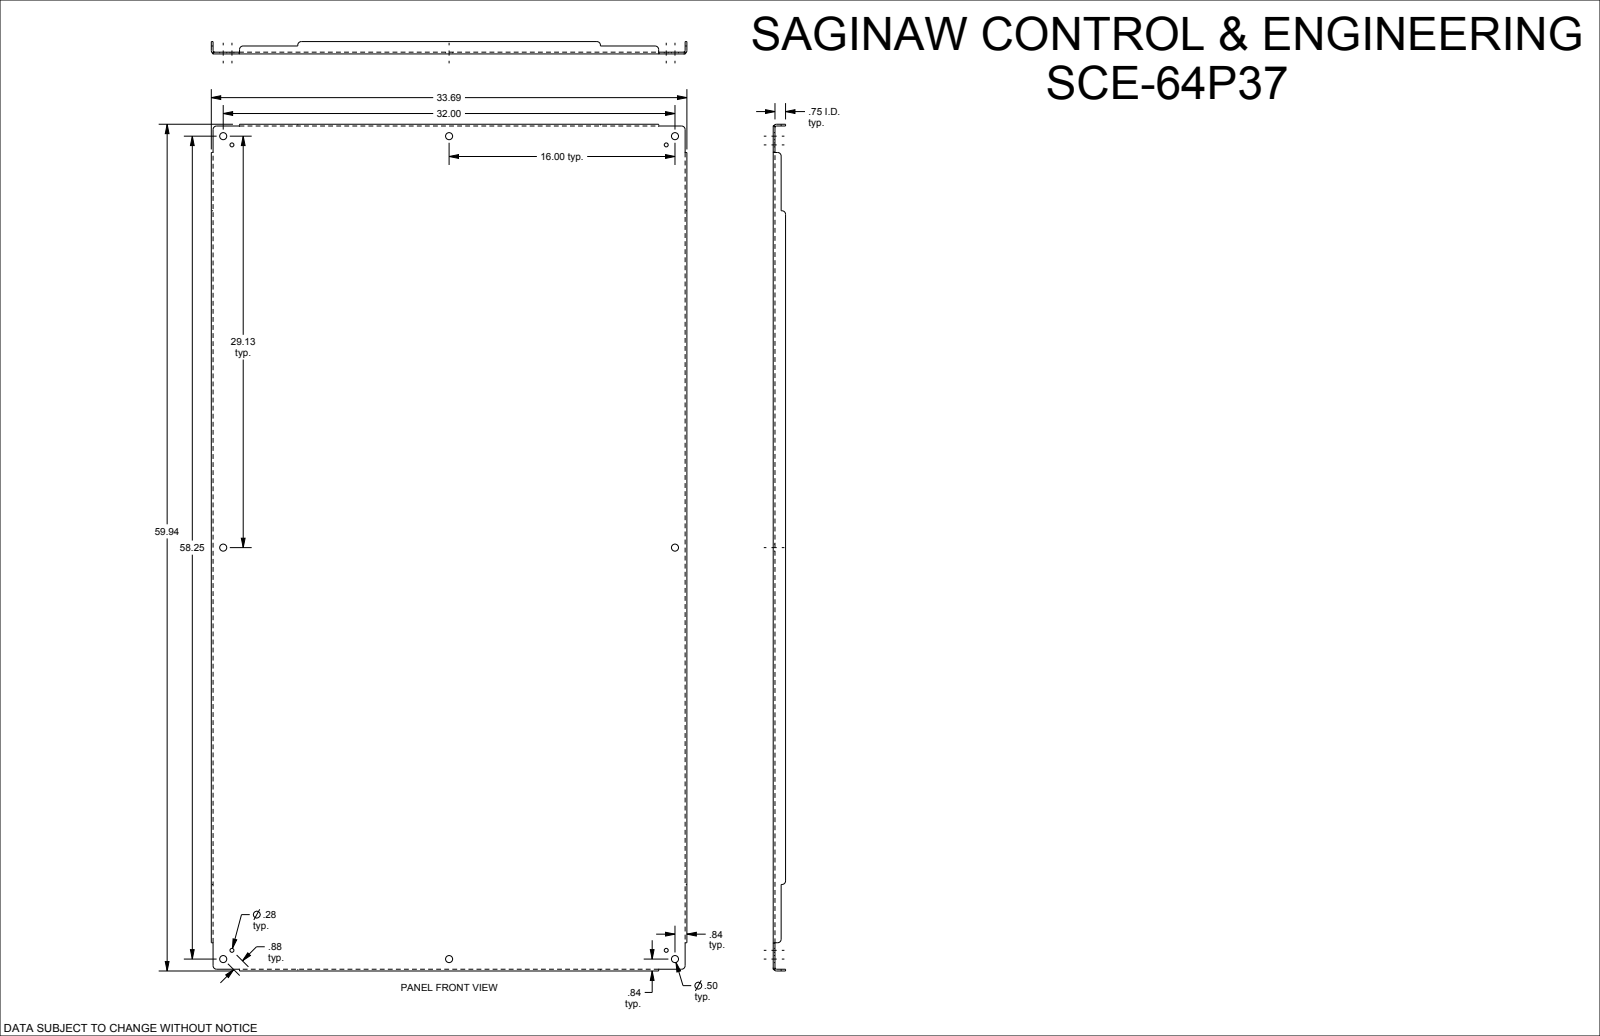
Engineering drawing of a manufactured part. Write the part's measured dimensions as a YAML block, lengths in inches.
part_name: "SCE-64P37"
step_written_by: "SolidWorks 2019 (CONFIG_CONTROL_DESIGN)"
units: inches
bodies: {solids: 1, faces: 110, planar: 46, cylindrical: 40, other: 24}
overall_size: [59.938, 33.688, 0.875]
volume: 265.1
surface_area: 4267
round_holes:
  - {diameter: 0.5, count: 8}
  - {diameter: 0.281, count: 4}
partial_cylinders:
  - {radius: 0.25, count: 12}
  - {radius: 0.112, count: 4}
  - {radius: 0.237, count: 4}
face_to_face_distances: [0.125, 33.563, 33.438, 33.687, 0.125, 59.813, 0.75, 0.875, 59.687, 59.938]
hole_center_spacings: [0.875, 15.394, 16, 28.513, 29.125, 31.387, 33.23, 42.396]
